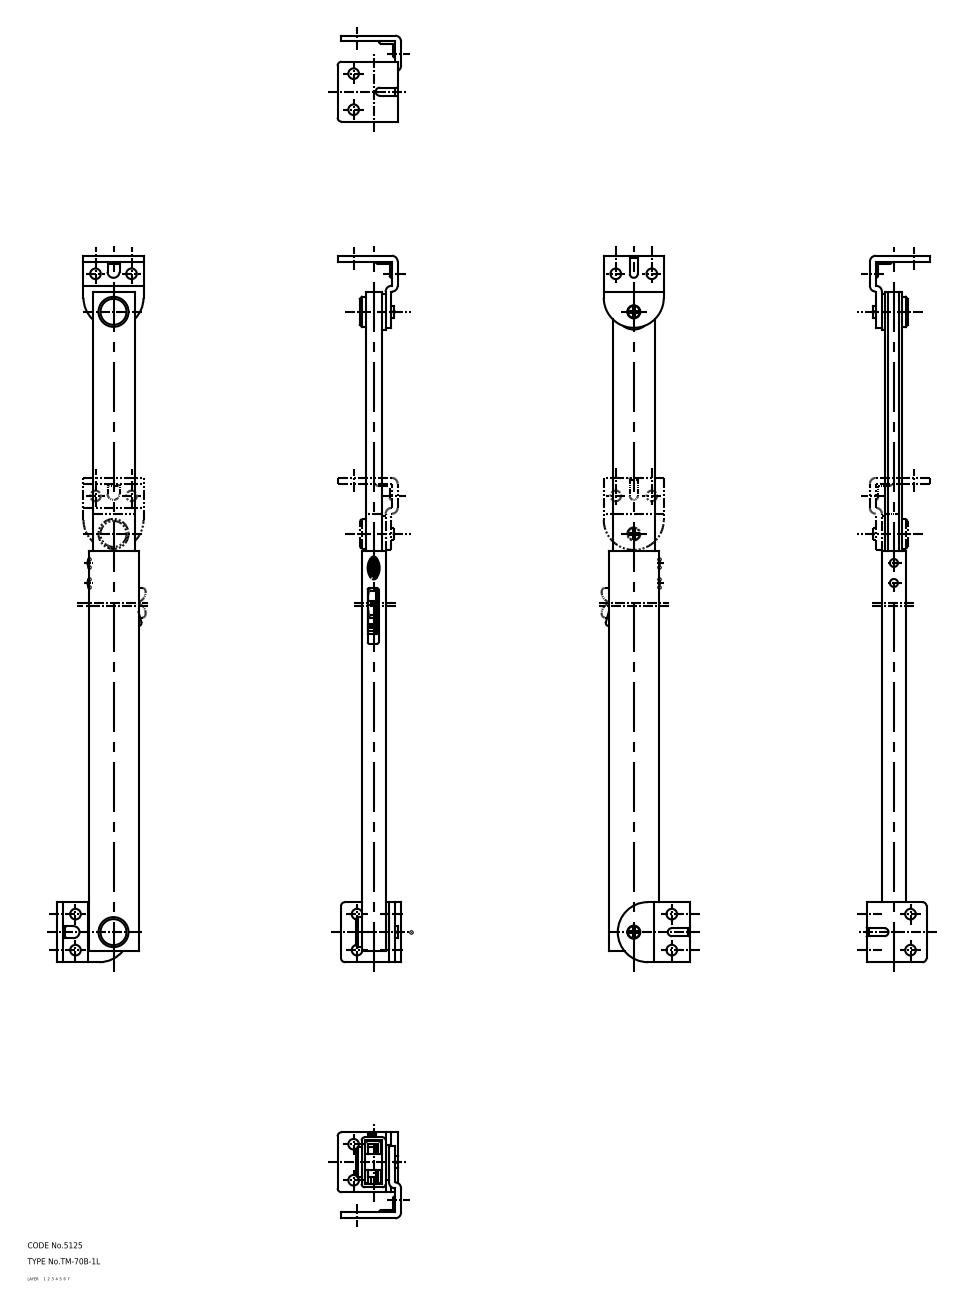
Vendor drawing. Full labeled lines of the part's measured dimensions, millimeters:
Part name (STEP PRODUCT): rivet_3_mr; rivet_2_mr; rivet_1_mr; bracket_A_mr (+7 more)
STEP written by: CADfix (AUTOMOTIVE_DESIGN)
Units: millimetres
Bodies: 12 solids, 282 faces (0 planar, 0 cylindrical, 282 other)
Overall size (bounding box): 353 × 43 × 31.7
Volume: 50 219 mm³ · Surface area: 58 445 mm²
